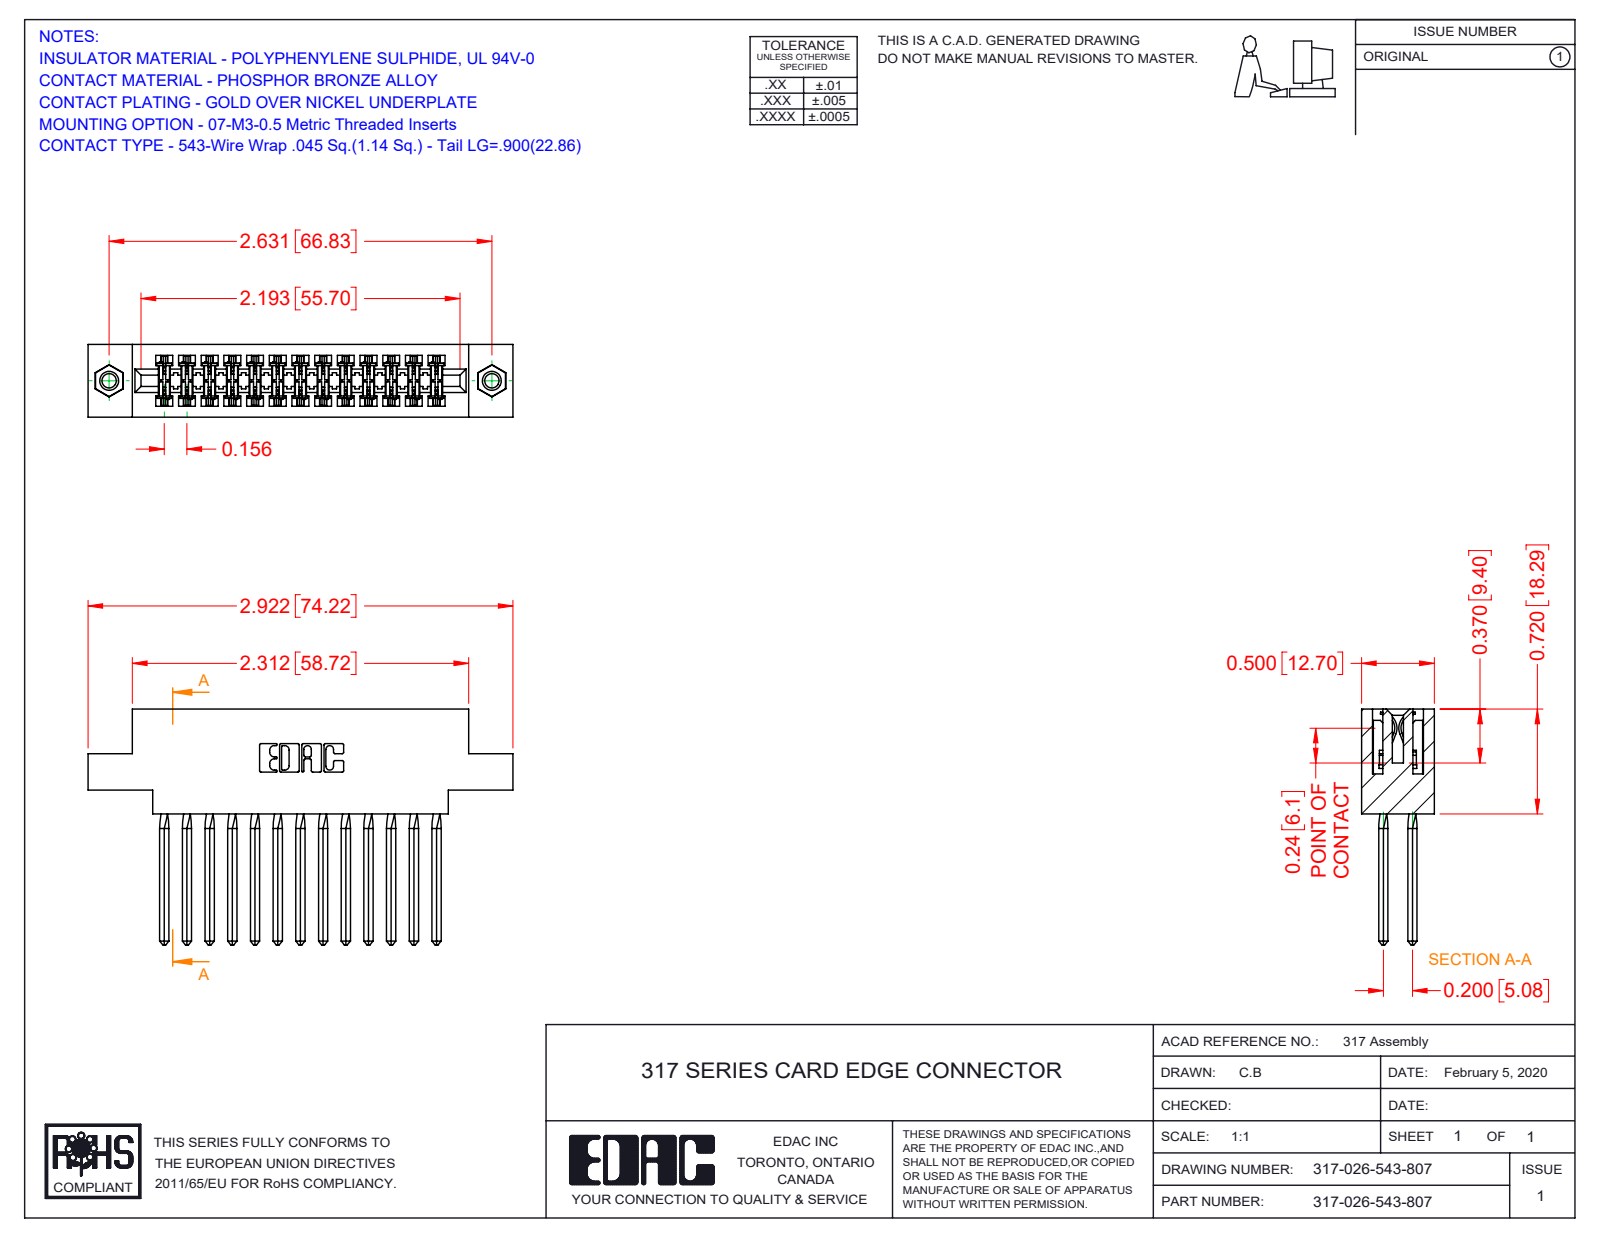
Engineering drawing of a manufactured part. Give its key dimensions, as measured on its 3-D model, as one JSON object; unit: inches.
{"part_name": "345-250-001_345-250-005-103; 317 Part_.156 Dia - TI; 317-290-001_543; 317-026-543-807", "step_written_by": "SolidWorks 2016 (CONFIG_CONTROL_DESIGN)", "units": "inches", "bodies": {"solids": 29, "faces": 2476, "planar": 1988, "cylindrical": 368, "other": 120}, "overall_size": [2.922, 1.62, 0.5], "volume_in3": 0.707, "surface_area_in2": 25.55, "round_holes": [[0.098, 2], [0.125, 2], [0.156, 2]], "round_bosses_or_shafts": [[0.155, 2]], "partial_cylinders_radius": [[0.015, 52], [0.01, 22], [0.007, 6], [0.031, 6], [0.026, 3], [0.095, 2], [0.1, 2], [0.11, 2]], "face_to_face_distances": [0.5, 0.075, 0.425, 0.11, 0.22, 0.35, 0.331, 0.136, 0.72, 0.305], "hole_center_spacings": [2.631]}
